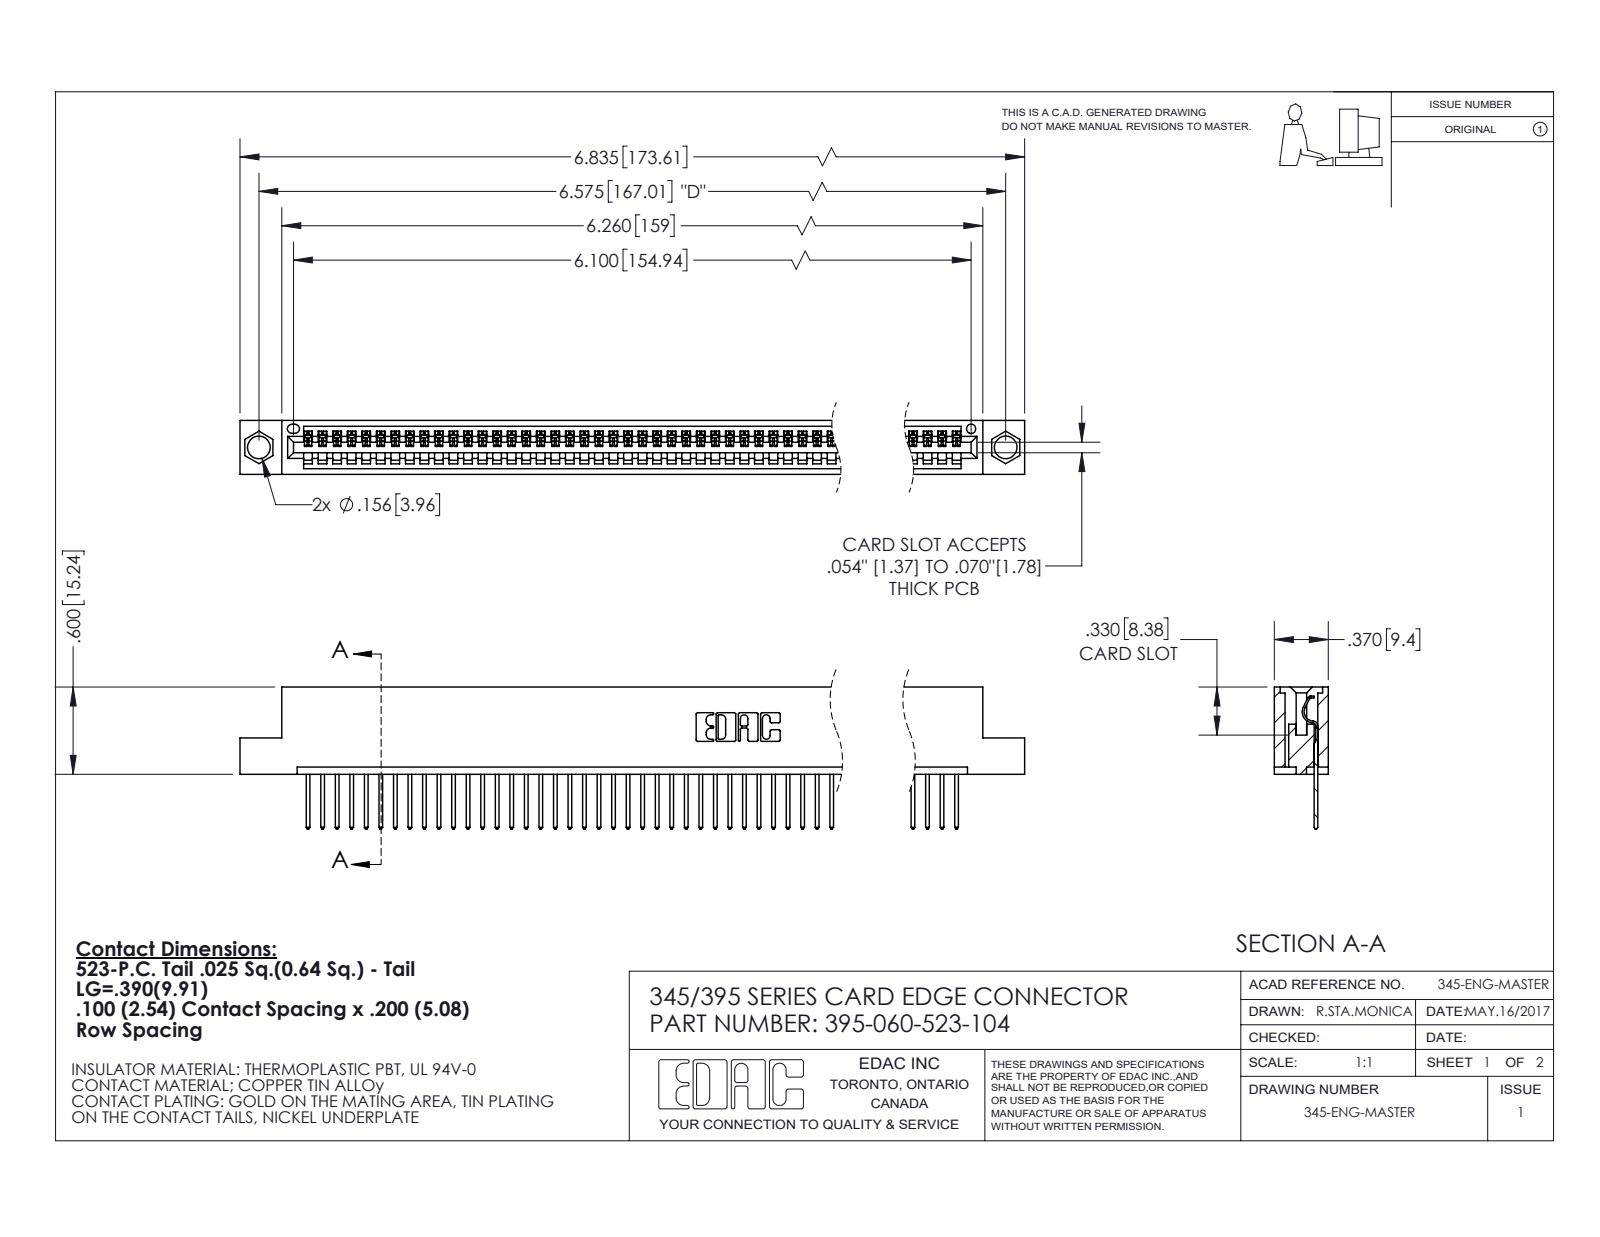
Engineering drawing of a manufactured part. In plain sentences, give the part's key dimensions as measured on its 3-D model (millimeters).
The part is named "345-292-001_345-293-123; 345 Part_Flush Mounting Lugs - 0.156 Dia-TI; 395-060-523-104". Its 3-D file was written by "SolidWorks 2020 (CONFIG_CONTROL_DESIGN)". It is 61 solids with 3620 faces: 2494 planar, 1126 cylindrical and 0 other. Overall it measures 173.6 by 24.8 by 9.4 millimeters. Its volume is 16 500 cubic millimeters and its surface area 22 090 square millimeters. Round holes: 2 of diameter 4, 1 of diameter 1.6. Partial cylindrical surfaces (rounded edges, fillets, slot ends): 120 of radius 0.2, 120 of radius 0.3, 22 of radius 0.3, 6 of radius 0.2, 6 of radius 0.8, 3 of radius 0.7, 2 of radius 0.8, 2 of radius 1. The main face-to-face distances are 7.6, 1.8, 9.4, 5.1, 2.5, 6.9, 0.6, 5.7, 3.8, 1.8. The hole center spacings are 6.9, 161, 167.
